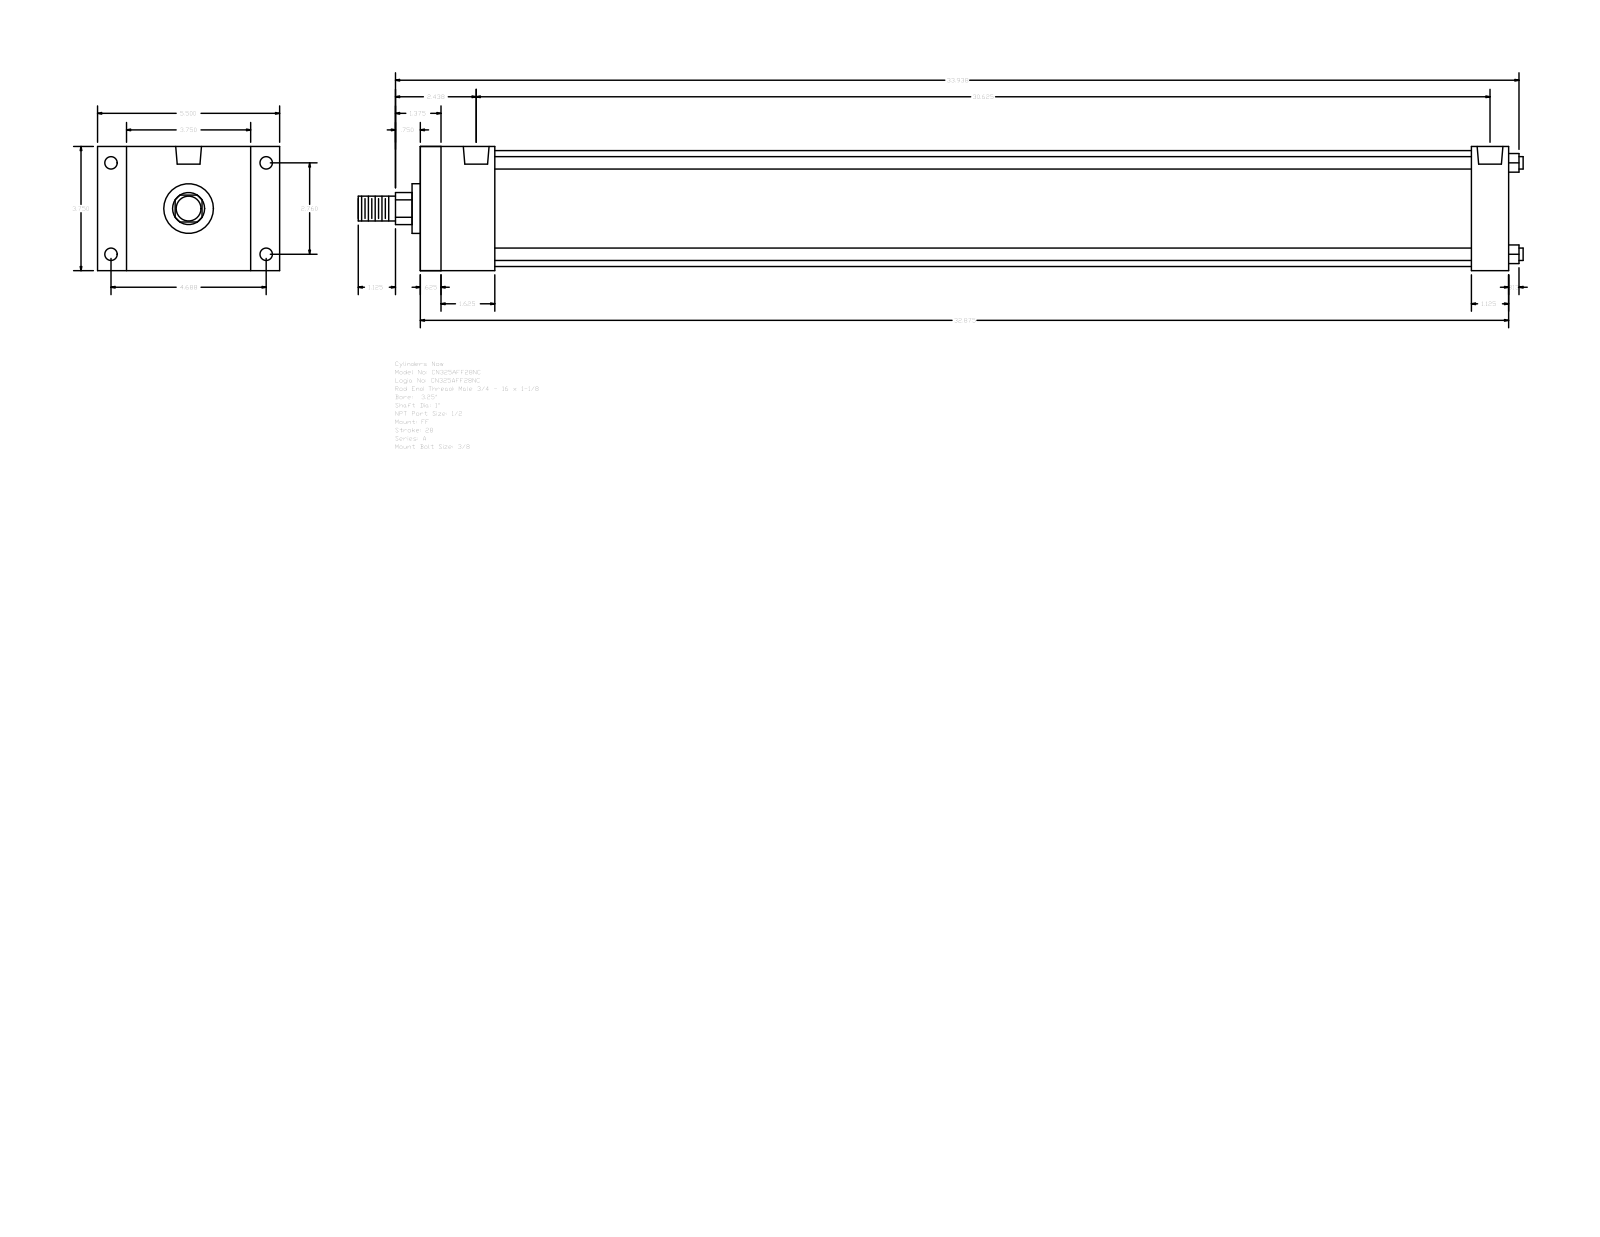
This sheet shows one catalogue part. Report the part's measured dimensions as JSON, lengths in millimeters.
{"part_name": "A_FF__0325_1", "step_written_by": "GSSL Pune (CONFIG_CONTROL_DESIGN)", "units": "millimeters", "bodies": {"solids": 0, "faces": 92, "planar": 64, "cylindrical": 28, "other": 0}, "overall_size": [893.76, 139.7, 95.25], "round_holes": [[8.73, 4], [9.53, 4], [19.77, 2]], "round_bosses_or_shafts": [[9.53, 4], [88.9, 1], [38.1, 1], [25.4, 1], [19.05, 1]], "partial_cylinders_radius": [[12.29, 1]], "face_to_face_distances": [95.24, 835.03, 15.87, 819.16, 22.23, 117.47, 57.15, 806.45, 41.28, 790.58], "hole_center_spacings": [3.18, 70.1, 119.06, 138.16, 771.52, 774.7, 777.88]}
